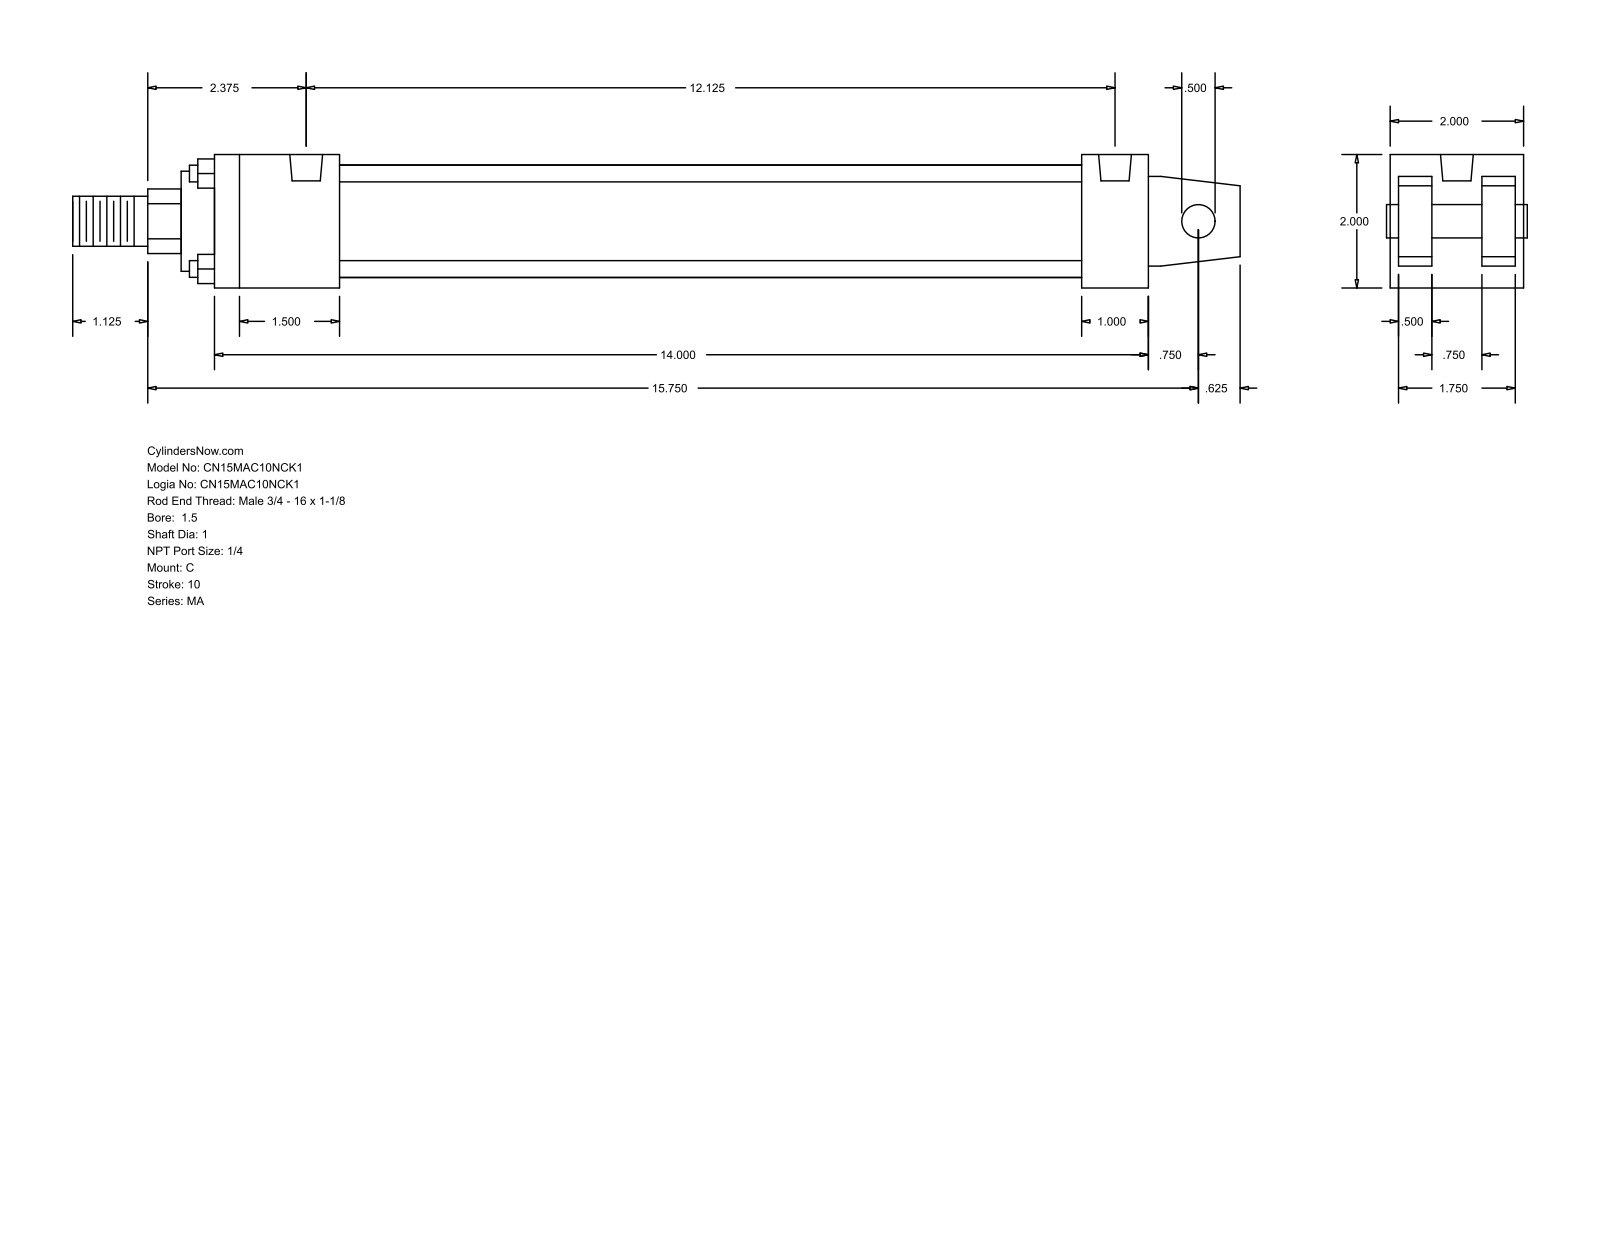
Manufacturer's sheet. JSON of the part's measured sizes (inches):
{"part_name": "MA_C__0150_1", "step_written_by": "GSSL Pune (CONFIG_CONTROL_DESIGN)", "units": "inches", "bodies": {"solids": 0, "faces": 103, "planar": 76, "cylindrical": 27, "other": 0}, "overall_size": [17.5, 2, 2], "round_holes": [[0.313, 4], [0.492, 2]], "round_bosses_or_shafts": [[0.25, 4], [1.69, 1], [1.5, 1], [1, 1], [0.75, 1], [0.5, 1]], "partial_cylinders_radius": [[0.484, 1]], "face_to_face_distances": [2, 1.875, 0.5, 1.375, 0.125, 0.625, 1.25, 2.375, 13.5, 14], "hole_center_spacings": [12.125]}
